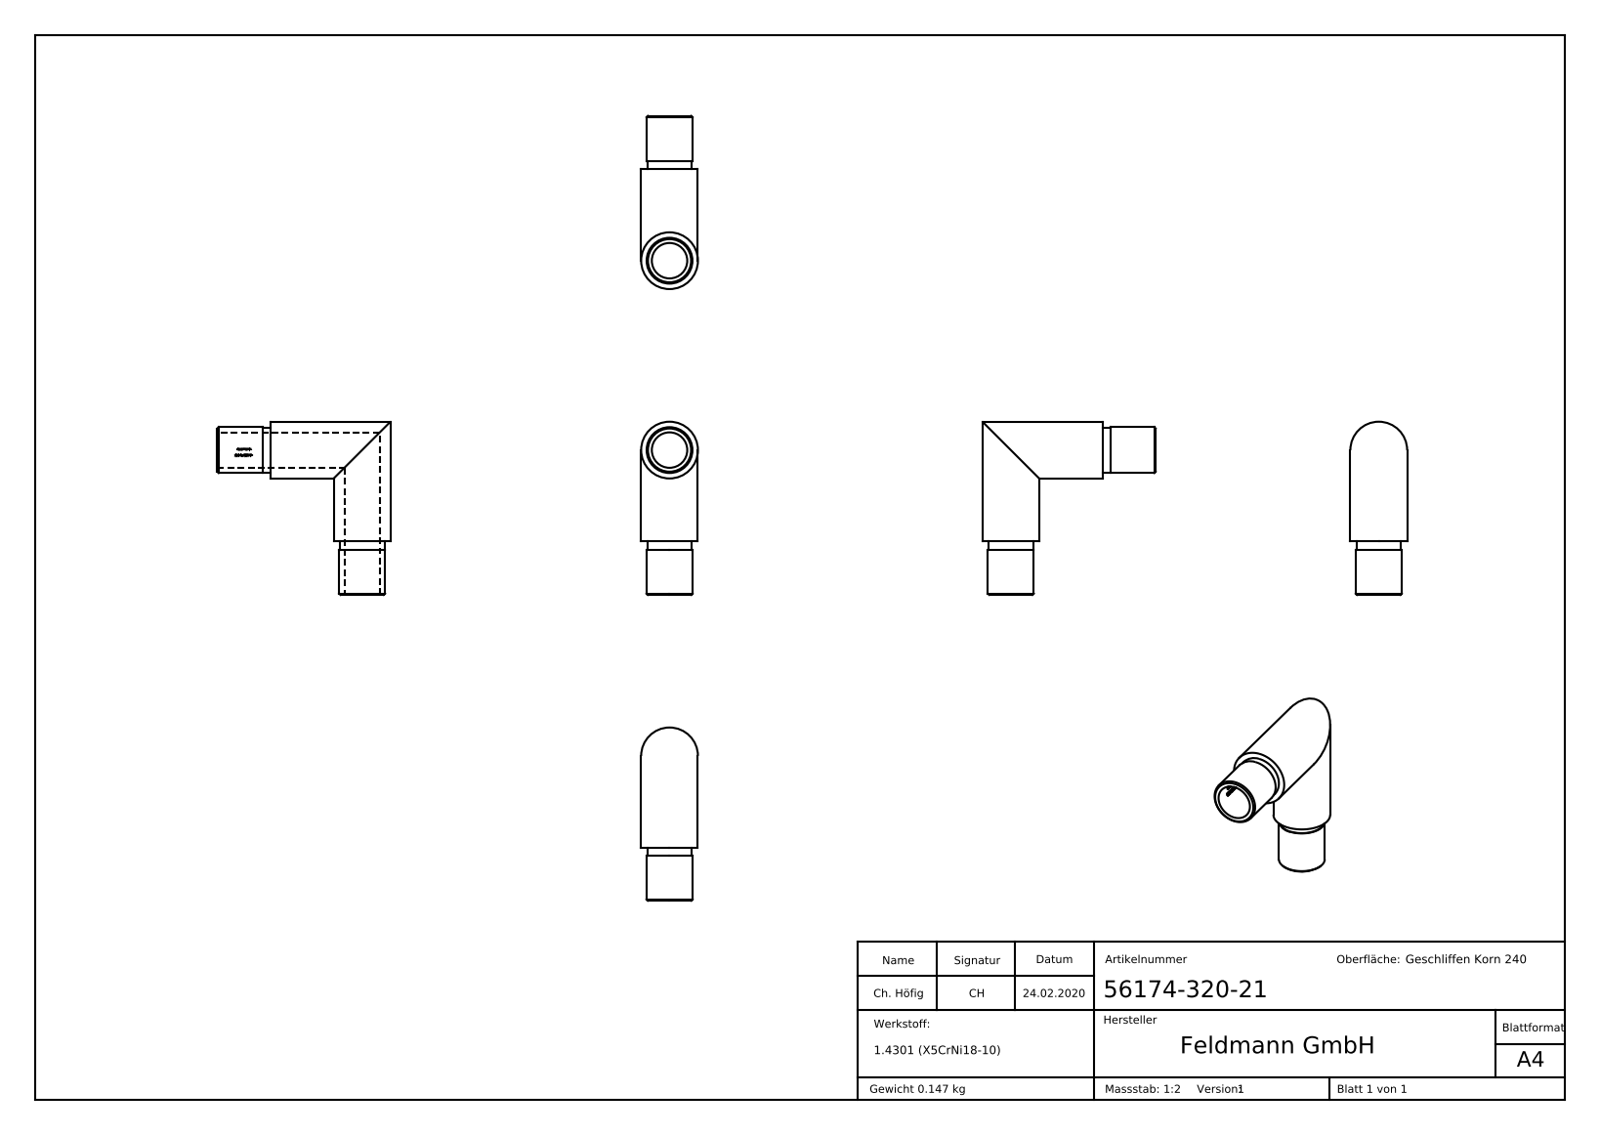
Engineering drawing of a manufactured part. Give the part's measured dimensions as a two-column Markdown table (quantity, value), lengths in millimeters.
| quantity | value |
| --- | --- |
| part name | 56174-320-21 |
| STEP written by | SolidWorks 2015 (CONFIG_CONTROL_DESIGN) |
| units | millimeters |
| bodies | 1 solid, 259 faces (123 planar, 34 cylindrical, 102 other) |
| overall size | 65 × 65 × 21.3 |
| volume | 18 595 mm³ |
| surface area | 11 744 mm² |
| round holes (diameter × count) | 13.3 × 2 |
| round bosses / shafts (diameter × count) | 21.3 × 2, 17.2 × 2, 16.8 × 2 |
| partial cylindrical surfaces (radius × count) | 6.75 × 1 |
| main face-to-face distances | 20, 17, 3, 0.79, 0.71, 2, 5, 4.44, 0.56, 0.45 |
